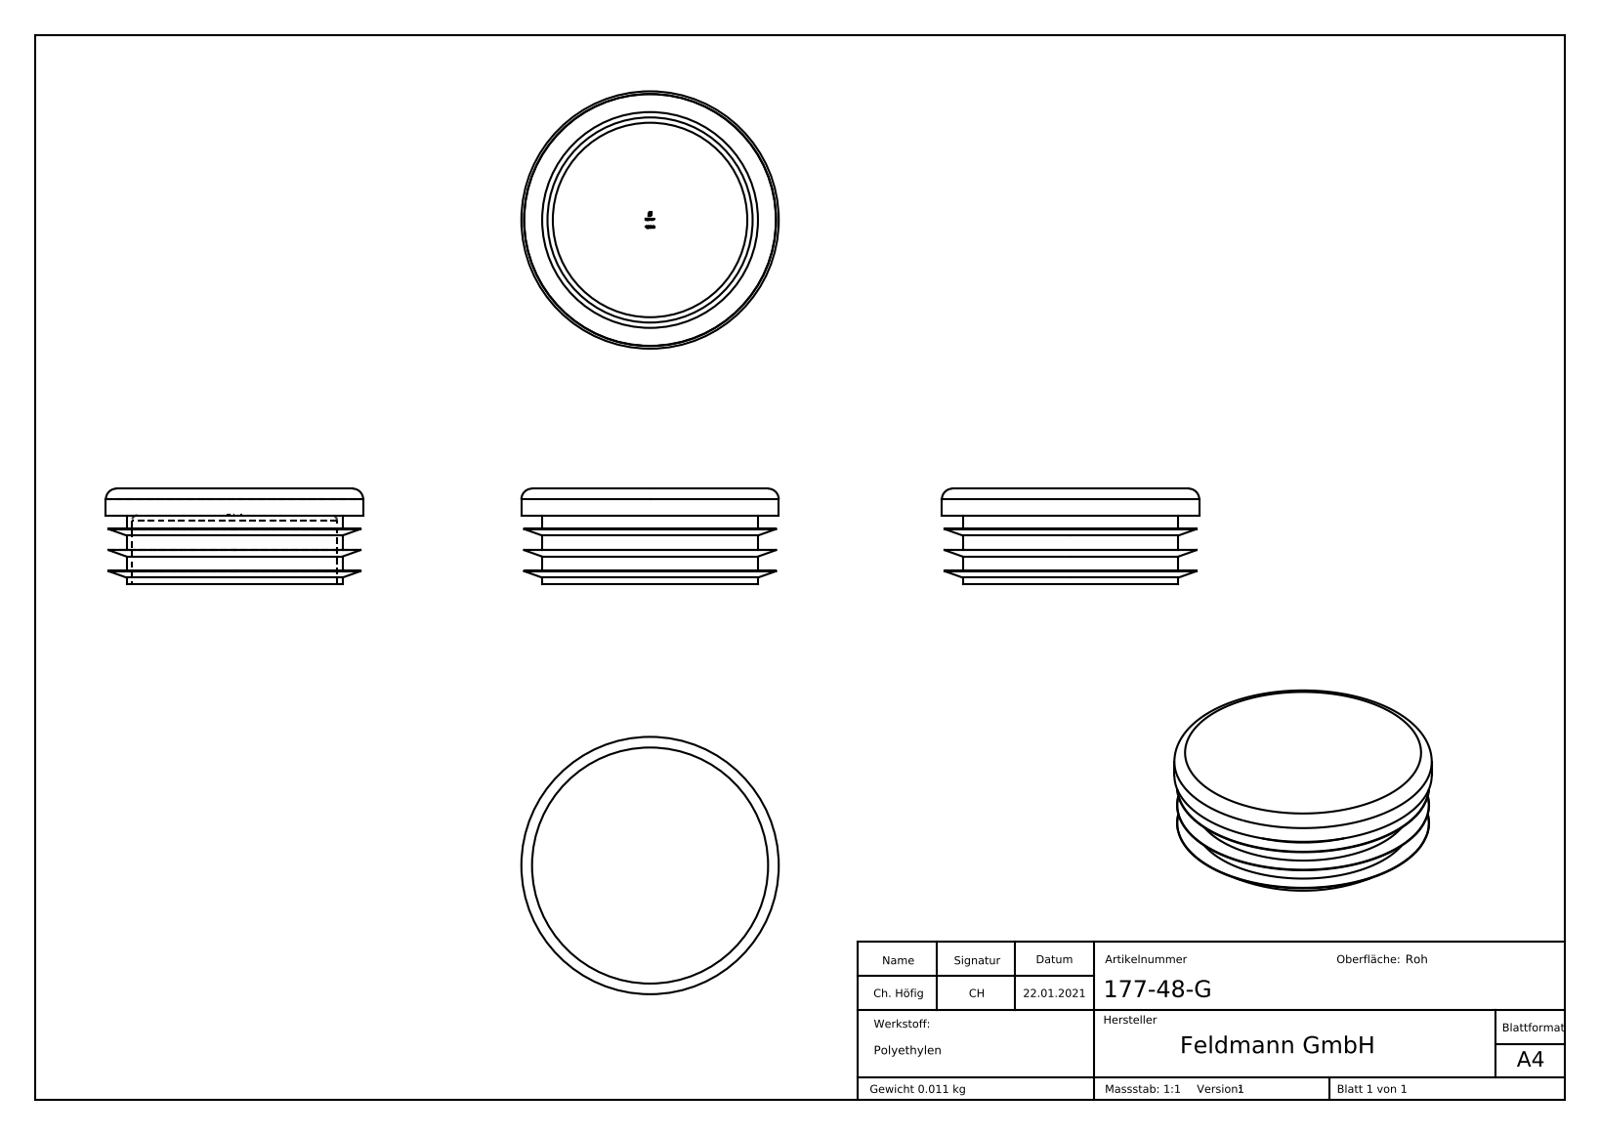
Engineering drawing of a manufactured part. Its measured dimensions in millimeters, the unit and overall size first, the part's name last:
Units: millimetres
Overall size (bounding box): 48.3 × 48.3 × 18
Round holes (diameter × count): ⌀38.5 ×1
Round bosses / shafts (diameter × count): ⌀48.3 ×1, ⌀40.5 ×1
Main face-to-face distances: 5, 3.95, 7.9, 10.4, 15.4, 6.45, 11.45, 2.5, 7.5, 2.6
Volume: 11 624 mm³ · Surface area: 9 896 mm²
Bodies: 1 solid, 269 faces (147 planar, 12 cylindrical, 110 other)
Part name (STEP PRODUCT): 177-48-G
STEP written by: SolidWorks 2018 (CONFIG_CONTROL_DESIGN)
